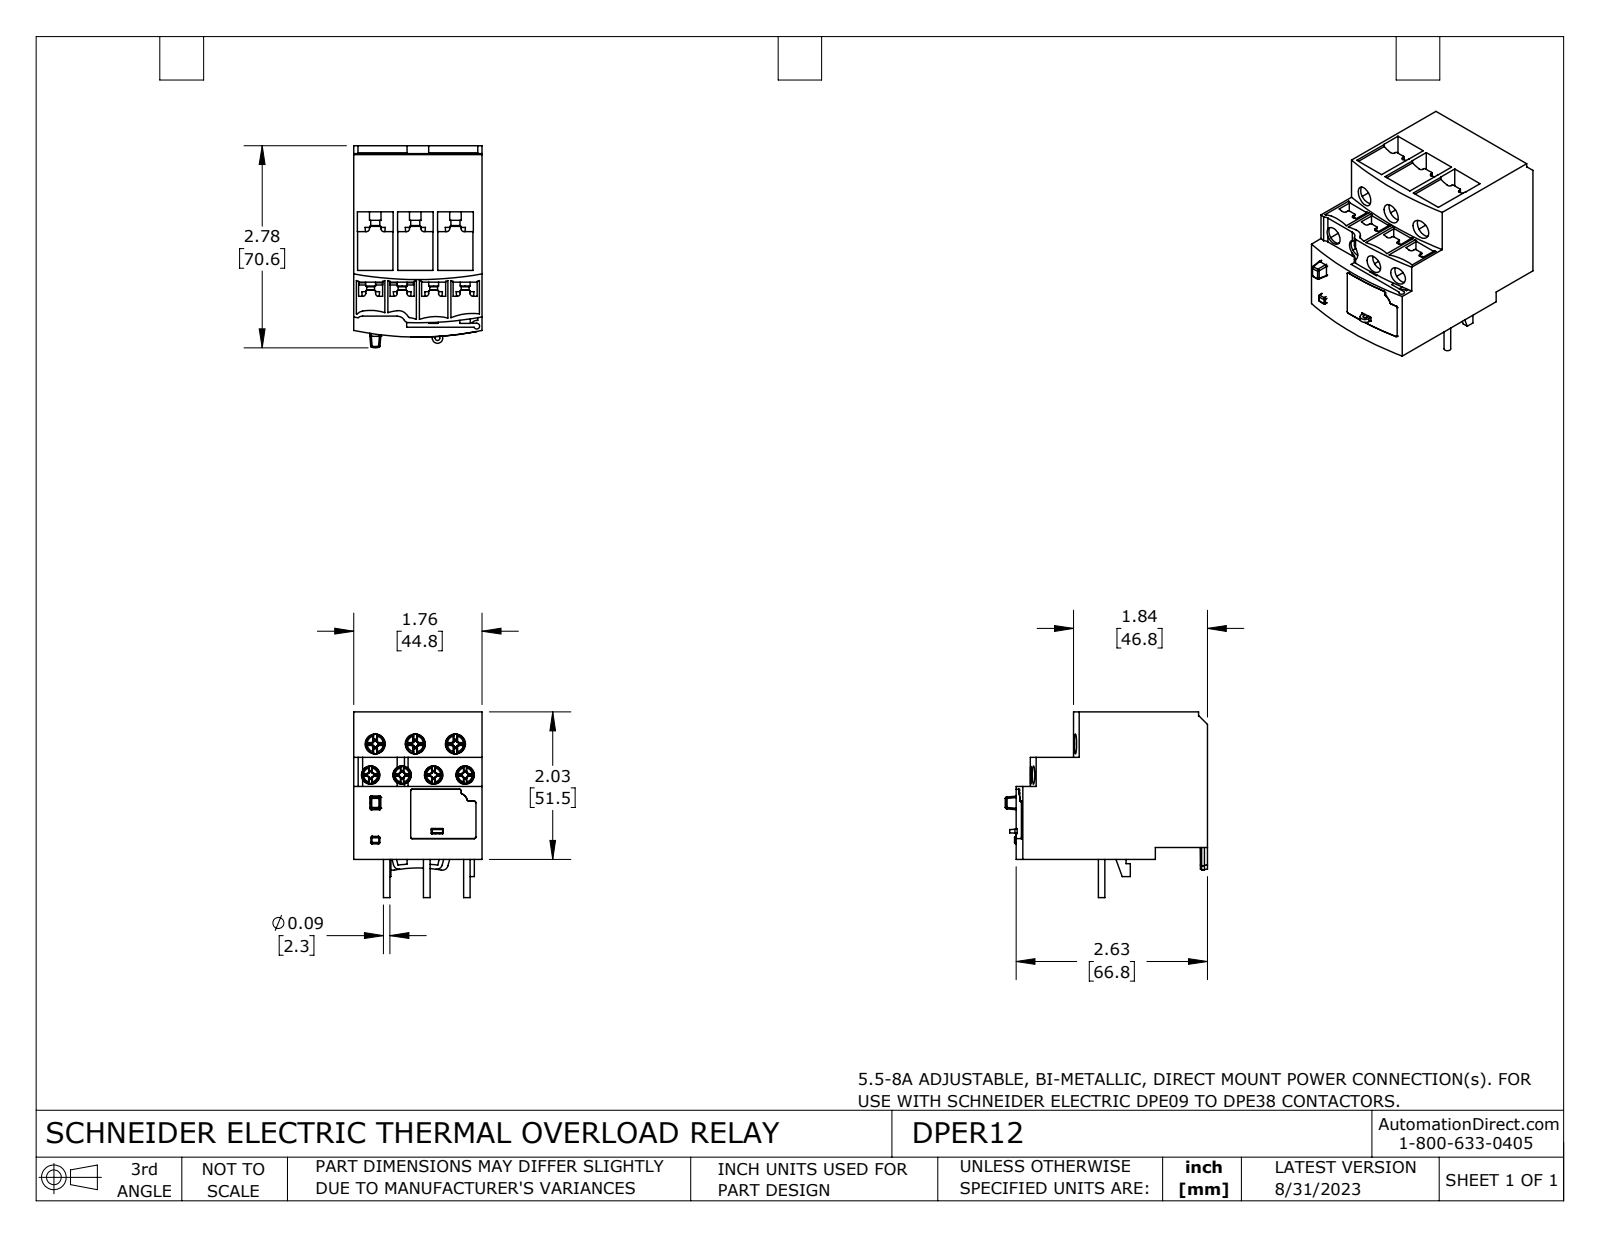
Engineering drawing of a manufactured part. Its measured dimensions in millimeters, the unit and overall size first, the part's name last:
Units: millimetres
Overall size (bounding box): 70.6 × 64.8 × 44.8
Round holes (diameter × count): ⌀6.4 ×4, ⌀7 ×3, ⌀2 ×2, ⌀3 ×2, ⌀1.5 ×1, ⌀6.2 ×1
Round bosses / shafts (diameter × count): ⌀2.3 ×12, ⌀3.5 ×4, ⌀2.7 ×4, ⌀4 ×3, ⌀3.9 ×3, ⌀3.1 ×3, ⌀3 ×1, ⌀2.7 ×1
Partial cylindrical surfaces — rounded edges, fillets, slot ends (radius × count): R0.5 ×52, R1 ×22, R0.1 ×19, R0.3 ×8, R0.2 ×6, R16 ×6, R2 ×4, R0.6 ×2
Main face-to-face distances: 44.8, 4.2, 51.5, 47.3, 23.1, 14, 15.7, 35.8, 31.6, 63.4
Hole centre spacings: 11, 14, 22, 8.5, 9.7, 10.3, 10.7, 11.4
Volume: 113 900 mm³ · Surface area: 30 420 mm²
Bodies: 16 solids, 1212 faces (676 planar, 269 cylindrical, 267 other)
Part name (STEP PRODUCT): DPER12
STEP written by: SolidWorks 2021 (CONFIG_CONTROL_DESIGN)
